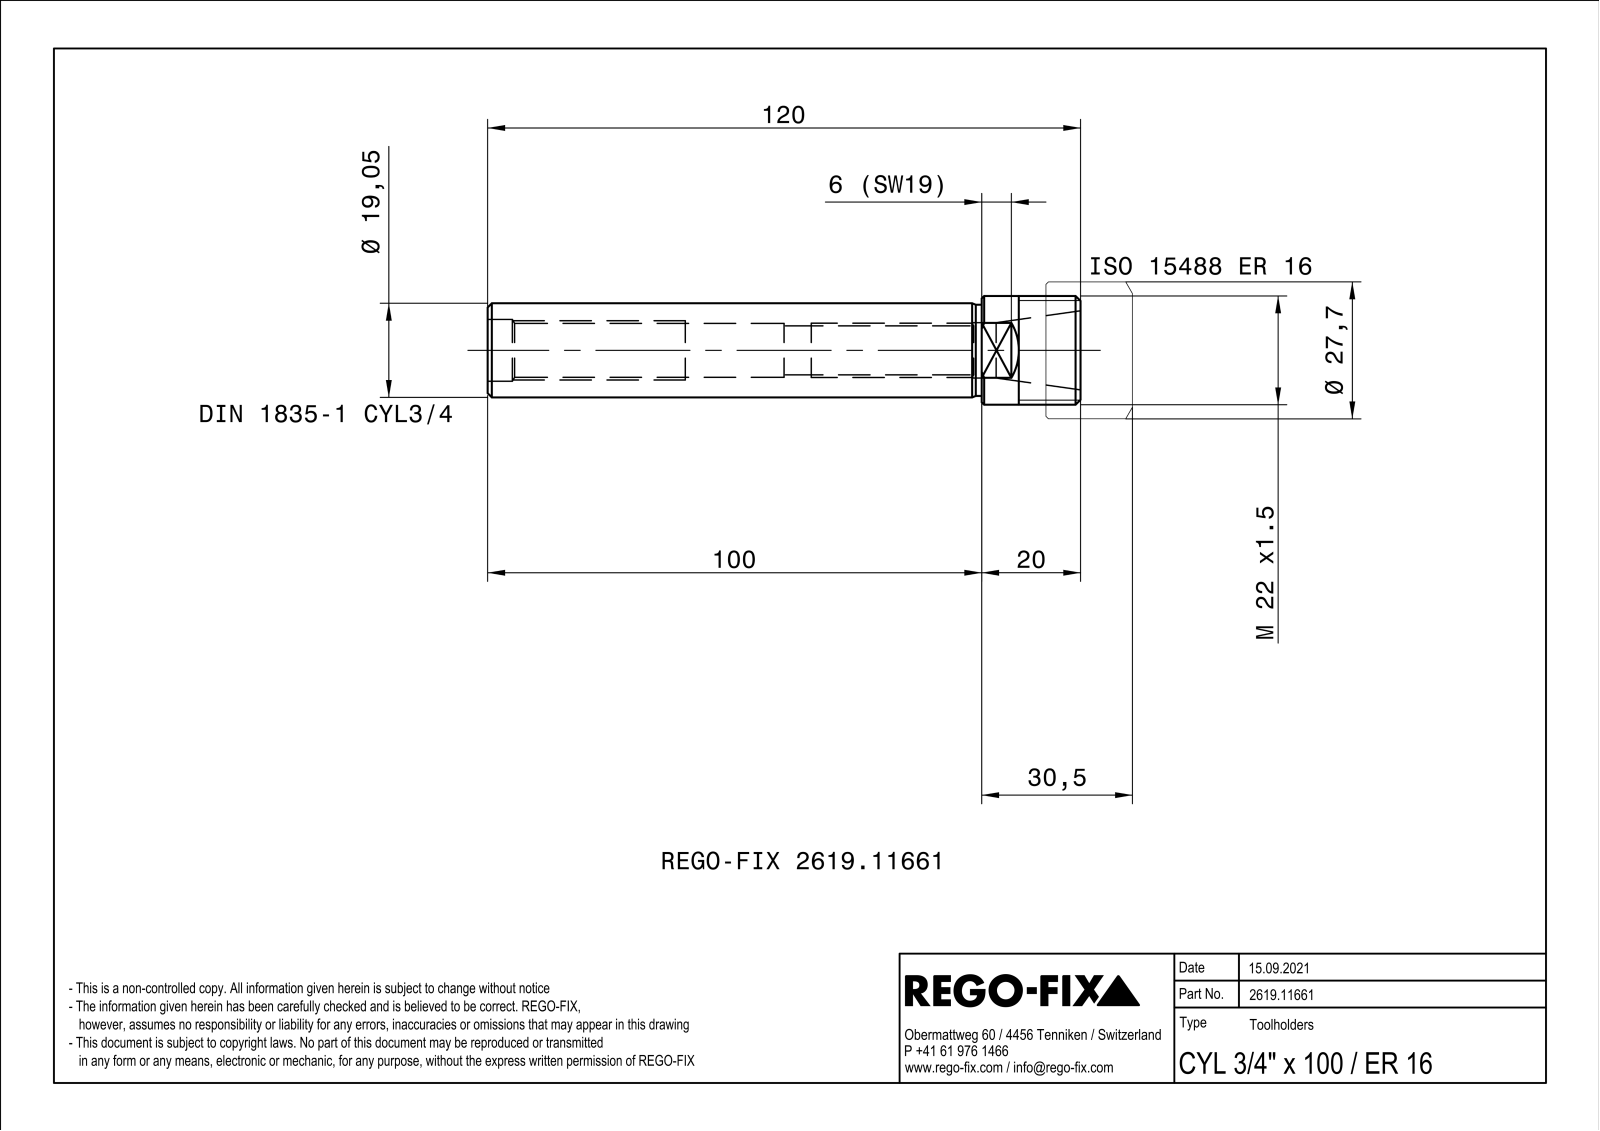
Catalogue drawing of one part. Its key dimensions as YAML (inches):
part_name: "NOCUT"
step_written_by: "SIEMENS PLM Software Solid Edge ST10 (AUTOMOTIVE_DESIGN)"
units: inches
bodies: {solids: 1, faces: 31, planar: 8, cylindrical: 11, other: 12}
overall_size: [4.724, 0.866, 0.866]
volume: 1.475
surface_area: 18.41
round_holes:
  - {diameter: 0.391, count: 1}
  - {diameter: 0.43, count: 1}
  - {diameter: 0.441, count: 1}
  - {diameter: 0.492, count: 1}
round_bosses_or_shafts:
  - {diameter: 0.866, count: 1}
  - {diameter: 0.75, count: 1}
  - {diameter: 0.734, count: 1}
face_to_face_distances: [4.724, 0.748, 0.787, 3.937]
